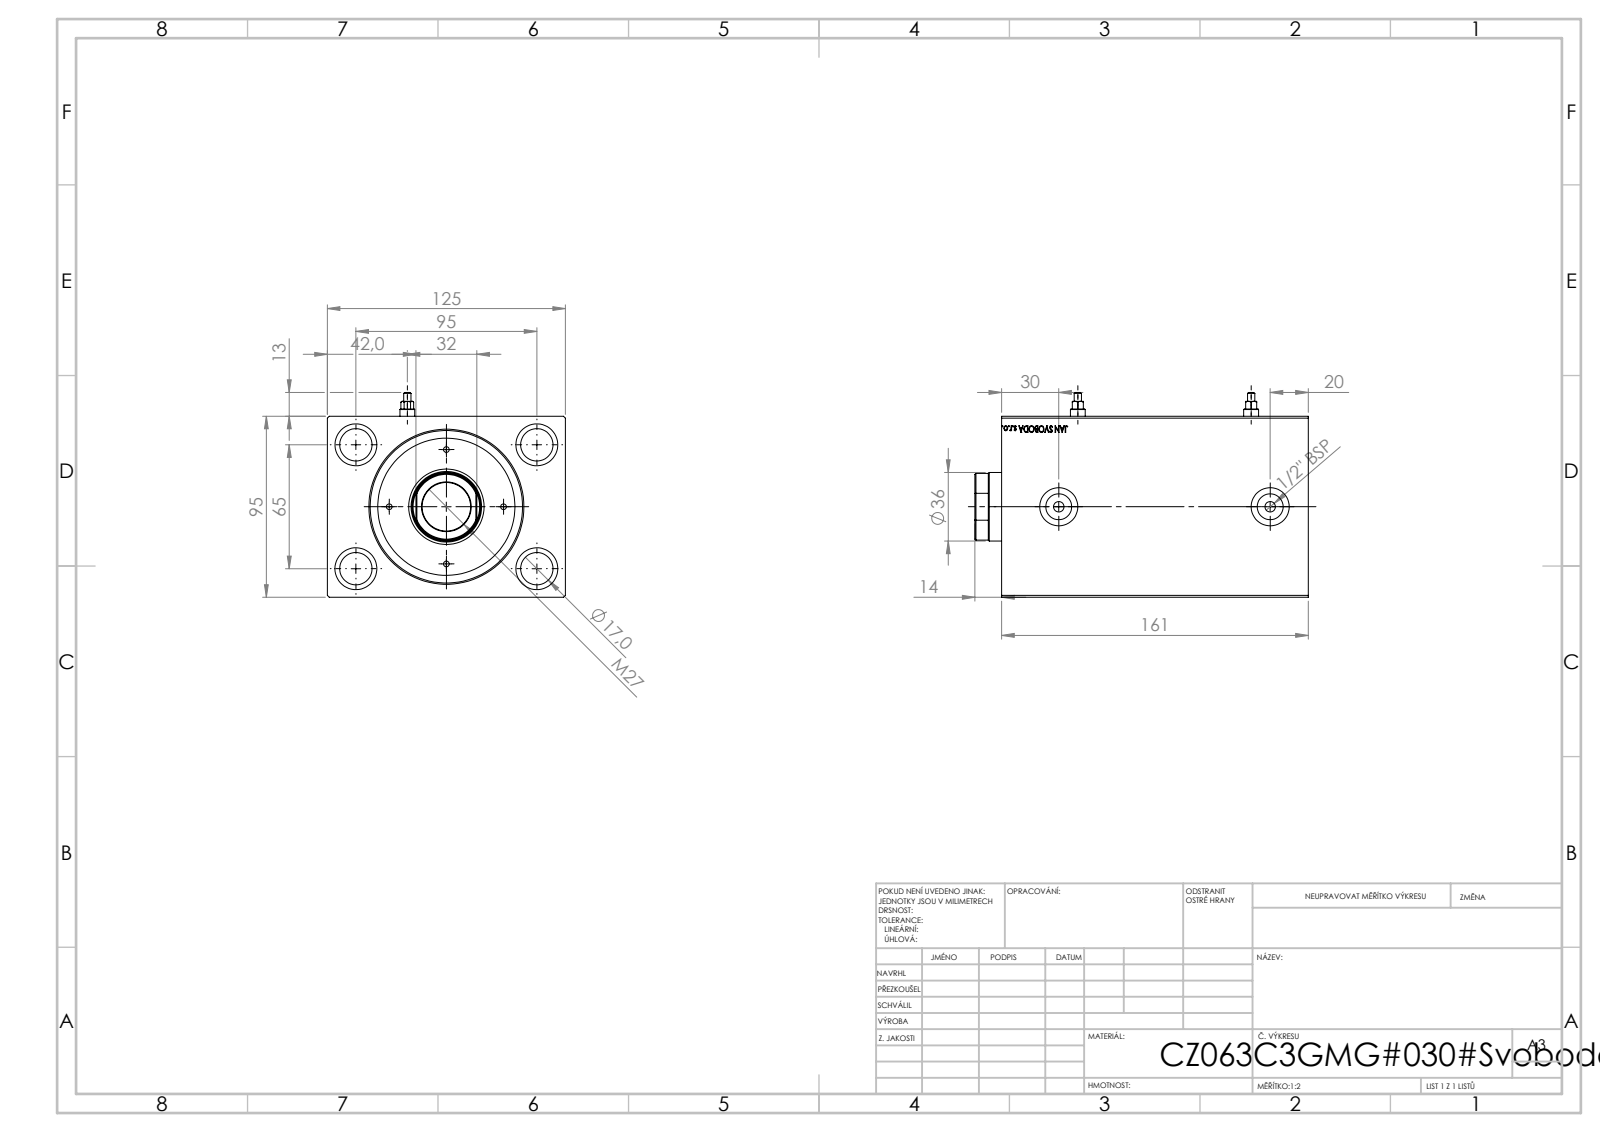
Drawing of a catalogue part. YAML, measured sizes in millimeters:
step_written_by: "SolidWorks 2019 (CONFIG_CONTROL_DESIGN)"
units: millimeters
bodies: {solids: 1, faces: 825, planar: 397, cylindrical: 46, other: 382}
overall_size: [161, 125, 95]
volume: 1284000
surface_area: 158111
round_holes:
  - {diameter: 17, count: 4}
  - {diameter: 22, count: 4}
  - {diameter: 5.5, count: 2}
  - {diameter: 8, count: 2}
  - {diameter: 13.6, count: 2}
  - {diameter: 20, count: 2}
  - {diameter: 36, count: 1}
  - {diameter: 63, count: 1}
  - {diameter: 80, count: 1}
face_to_face_distances: [95, 125, 161, 140.2, 20.8, 14, 126.2, 147, 10.33, 150.67]
hole_center_spacings: [57.55, 65, 95, 115.11, 91, 111]
